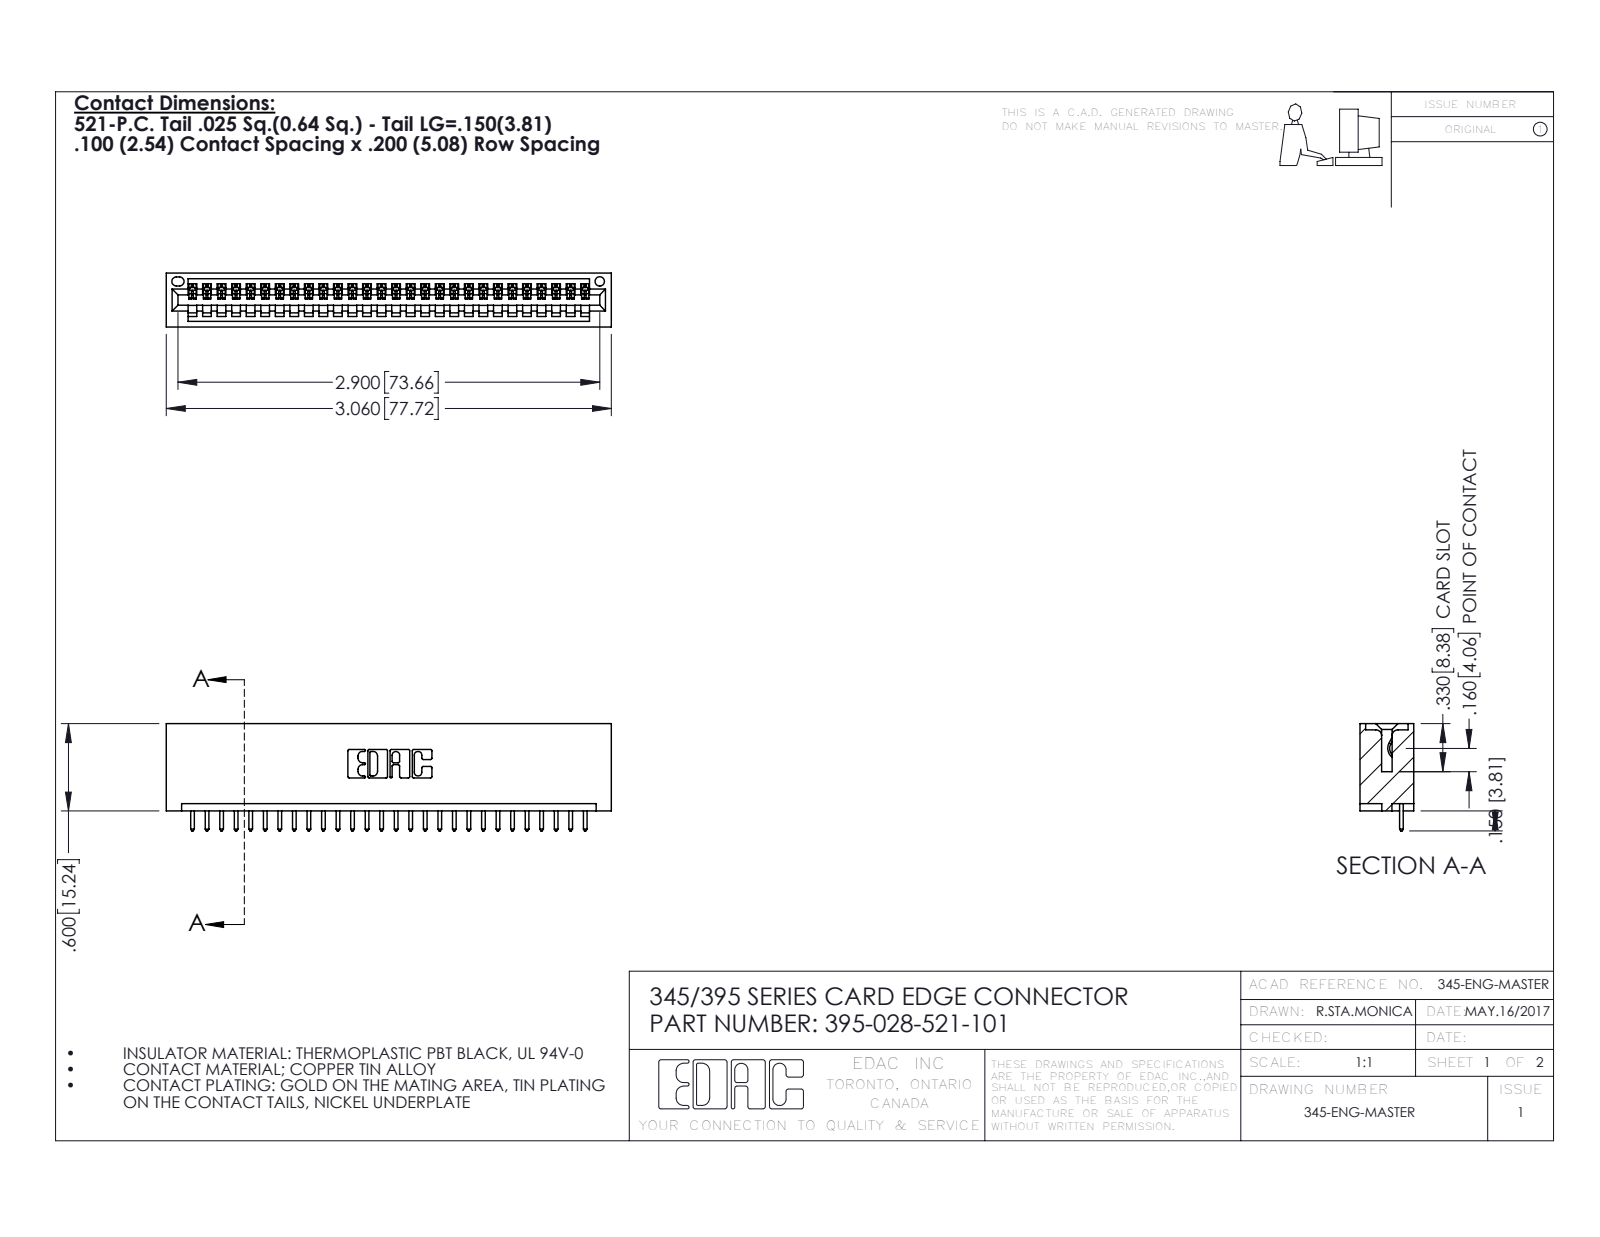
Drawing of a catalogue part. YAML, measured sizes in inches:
part_name: "345 Part_No Mounting Lugs; 395-028-521-101; 345-292-001_345-293-121"
step_written_by: "SolidWorks 2016 (CONFIG_CONTROL_DESIGN)"
units: inches
bodies: {solids: 29, faces: 1742, planar: 1196, cylindrical: 546, other: 0}
overall_size: [3.06, 0.737, 0.37]
volume: 0.474
surface_area: 15.53
round_holes:
  - {diameter: 0.064, count: 1}
partial_cylinders:
  - {radius: 0.006, count: 56}
  - {radius: 0.01, count: 56}
  - {radius: 0.01, count: 22}
  - {radius: 0.007, count: 6}
  - {radius: 0.031, count: 6}
  - {radius: 0.026, count: 3}
  - {radius: 0.031, count: 2}
  - {radius: 0.04, count: 2}
face_to_face_distances: [0.298, 0.072, 0.2, 0.37, 0.098, 0.272, 0.025, 0.225, 0.149, 0.072]
